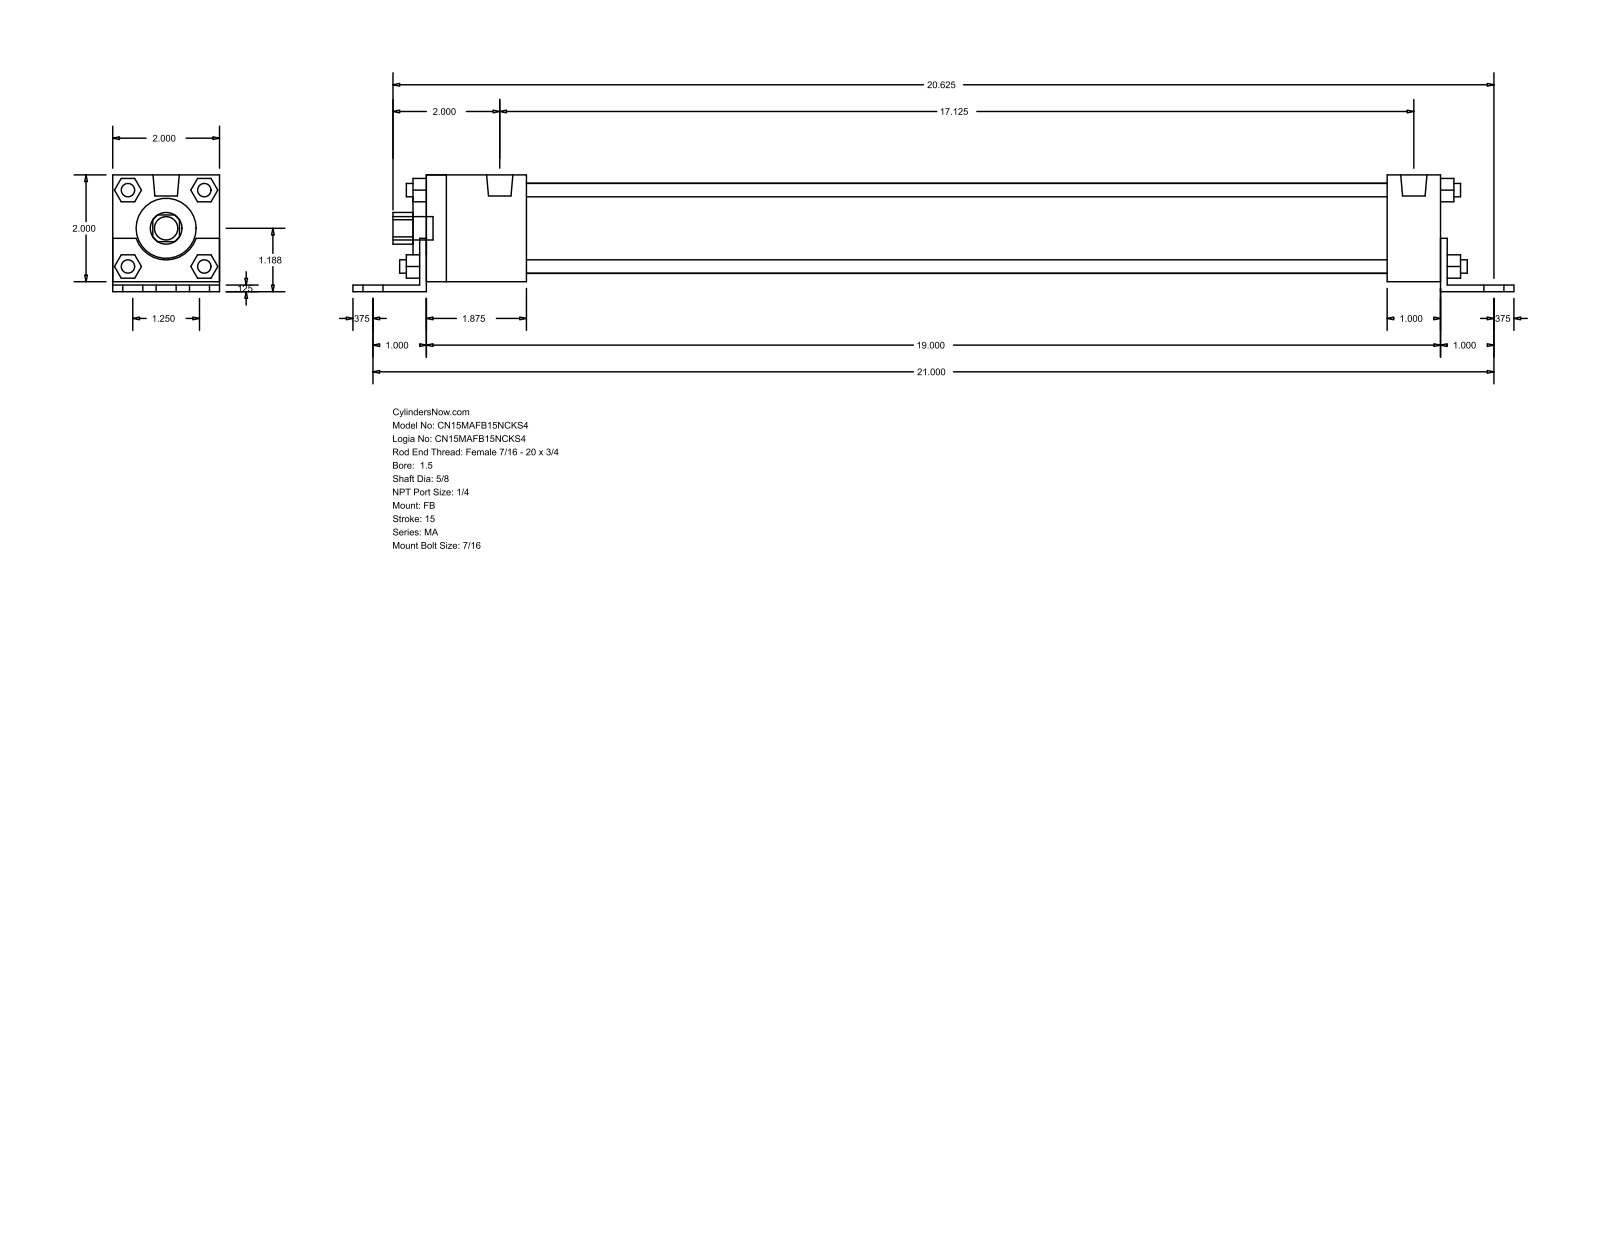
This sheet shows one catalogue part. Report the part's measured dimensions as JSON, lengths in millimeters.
{"part_name": "MA_FB__0150_0.625", "step_written_by": "GSSL Pune (CONFIG_CONTROL_DESIGN)", "units": "millimeters", "bodies": {"solids": 0, "faces": 140, "planar": 105, "cylindrical": 35, "other": 0}, "overall_size": [552.45, 55.56, 50.8], "round_holes": [[15.88, 1], [28.57, 1], [42.93, 1]], "round_bosses_or_shafts": [[11.11, 7], [7.94, 4], [6.35, 4], [12.49, 2]], "partial_cylinders_radius": [[7.54, 1], [15.05, 1]], "face_to_face_distances": [50.8, 3.17, 4.76, 55.56, 1.59, 52.39, 488.95, 3.18, 482.6, 28.58]}
